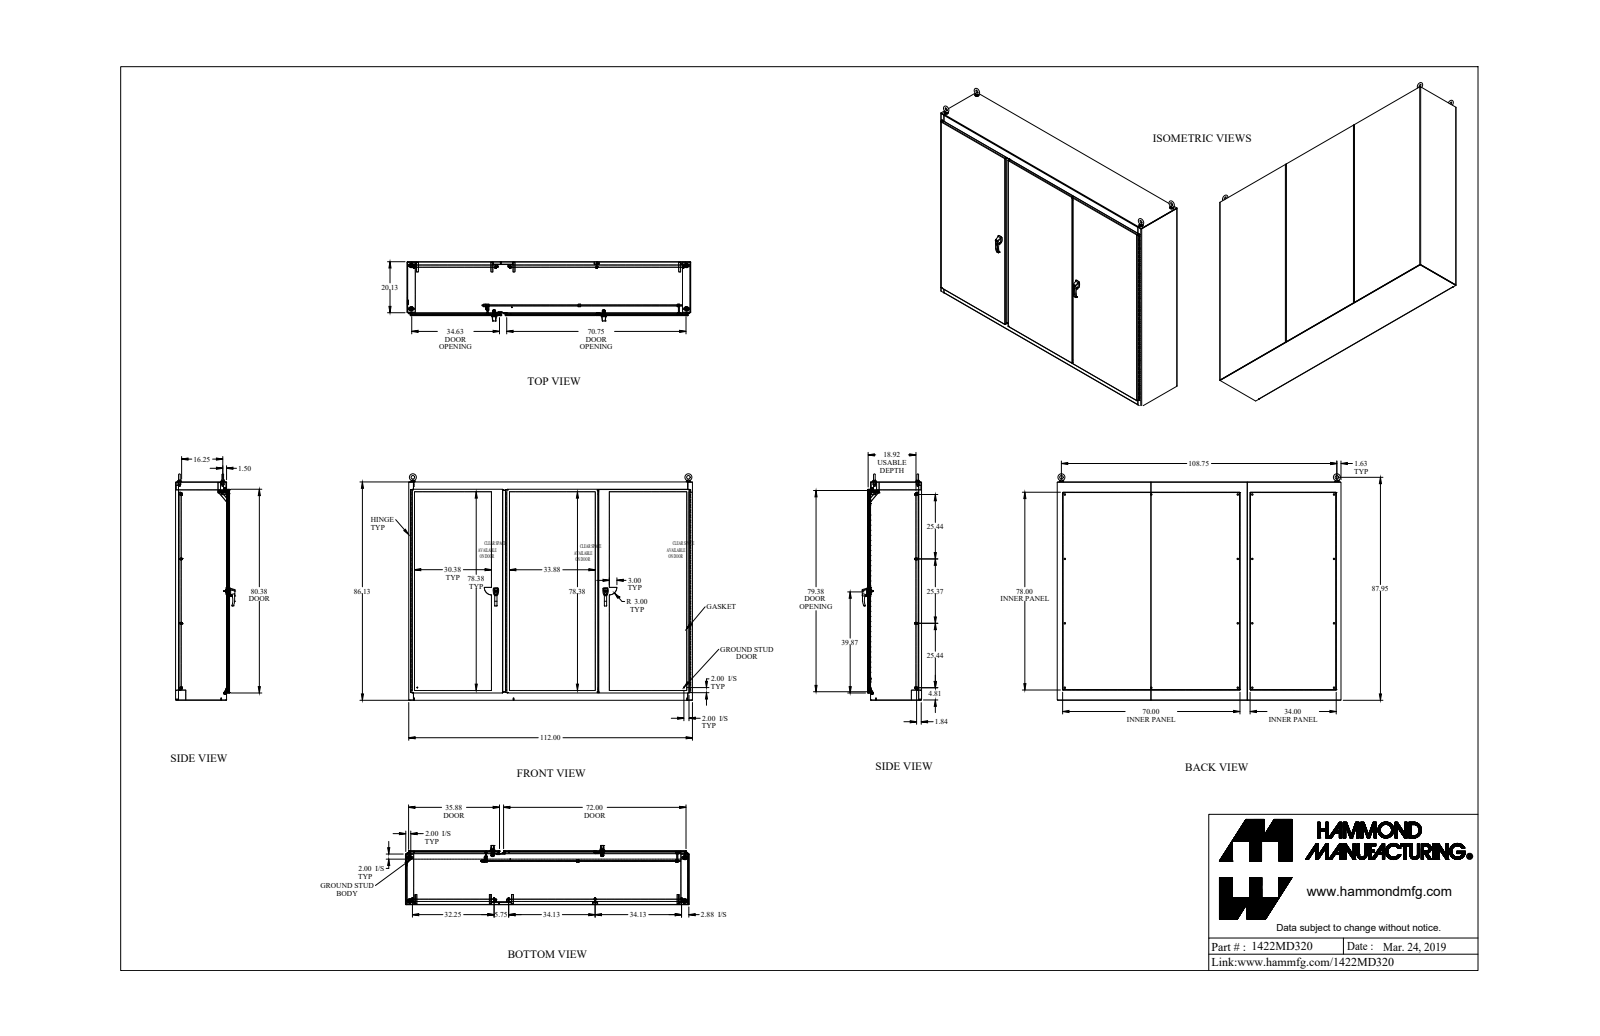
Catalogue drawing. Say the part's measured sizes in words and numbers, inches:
The part is named "1422MD320_Default". Its 3-D file was written by "SolidWorks 2019 (CONFIG_CONTROL_DESIGN)". It is 181 solids with 5208 faces: 2311 planar, 2412 cylindrical and 485 other. Overall it measures 112 by 89.778 by 23.402 inches. Its volume is 5 231 cubic inches and its surface area 82 415 square inches. Round holes: 42 of diameter 0.304, 18 of diameter 0.307, 18 of diameter 0.563, 14 of diameter 0.445, 6 of diameter 0.281, 5 of diameter 0.25, 5 of diameter 0.39, 5 of diameter 0.687, 4 of diameter 0.257, 4 of diameter 0.28, 4 of diameter 0.313, 4 of diameter 0.413. Round bosses or shafts: 23 of diameter 1, 19 of diameter 0.375, 18 of diameter 0.65, 18 of diameter 0.33, 10 of diameter 0.281, 6 of diameter 0.25, 4 of diameter 1.75, 4 of diameter 1.5. Partial cylindrical surfaces (rounded edges, fillets, slot ends): 62 of radius 0.06, 53 of radius 0.185, 43 of radius 0.125, 32 of radius 0.017, 12 of radius 0.03, 12 of radius 0.05, 12 of radius 0.09, 12 of radius 0.318. The main face-to-face distances are 0.125, 19.1, 21.162, 2.062, 0.125, 21.287, 18.975, 2.187, 19.225, 21.162. The hole center spacings are 6, 72.082, 12, 72.828, 18, 74.053, 24, 75.735.
